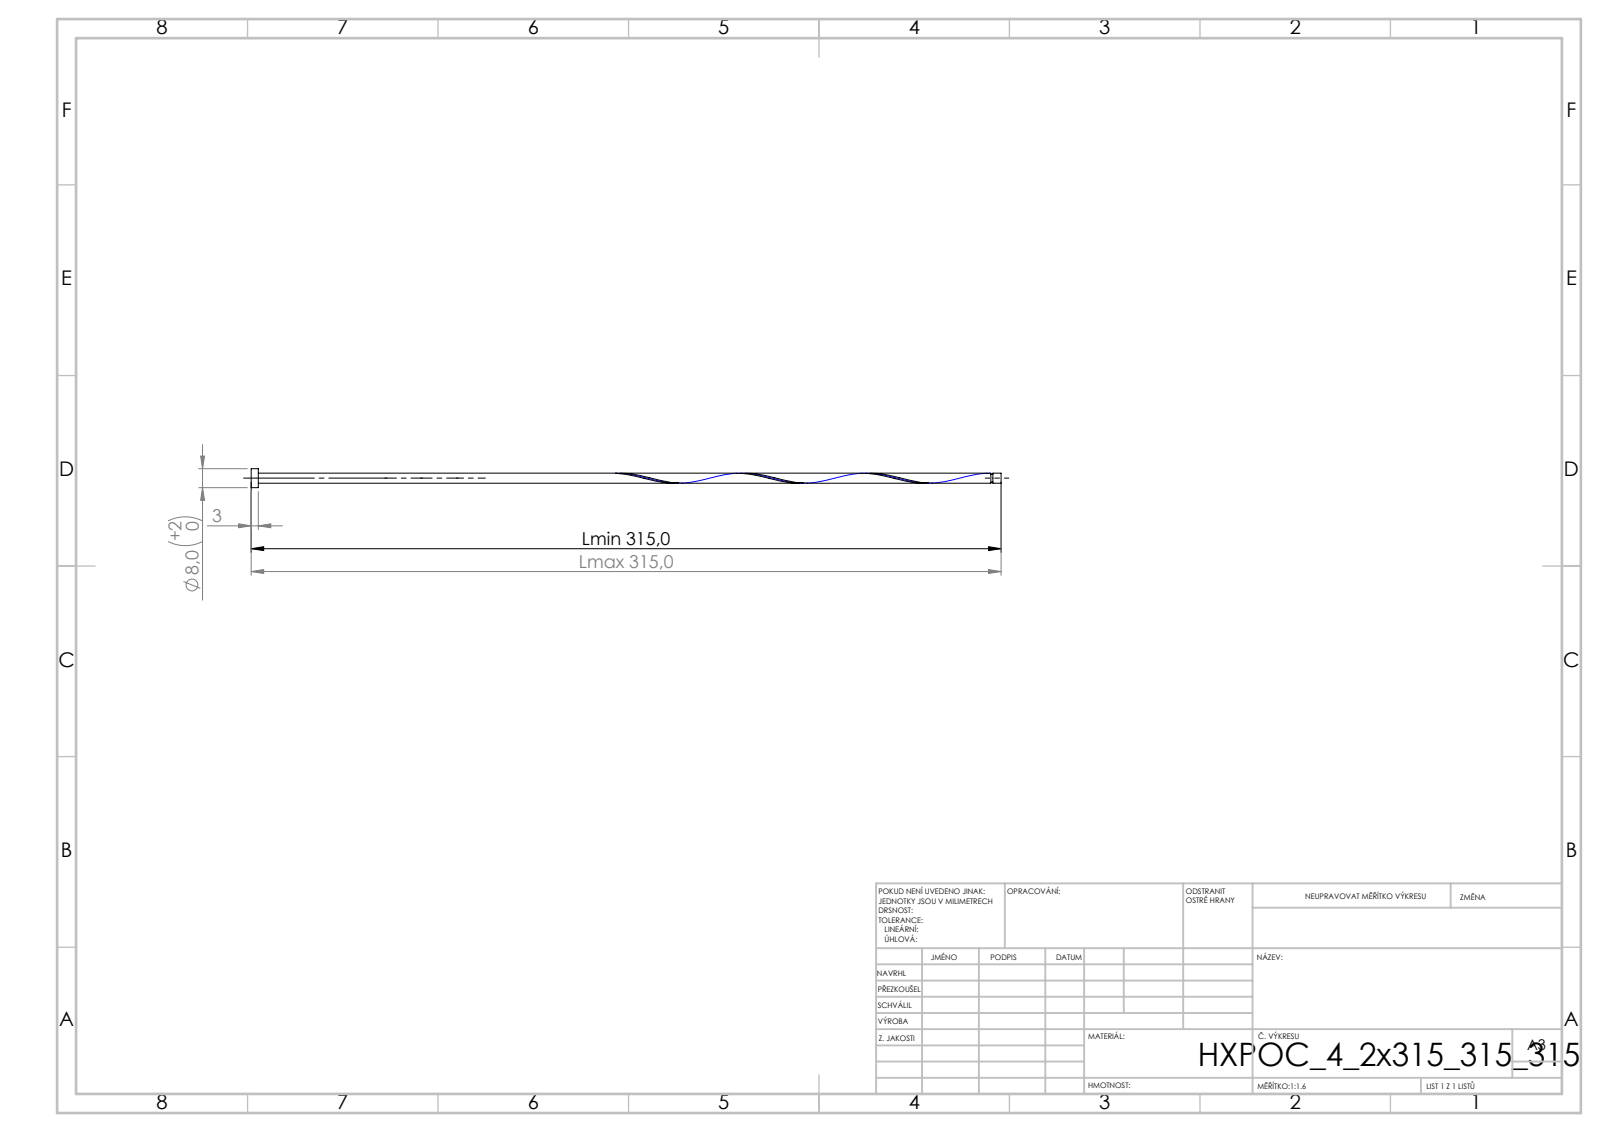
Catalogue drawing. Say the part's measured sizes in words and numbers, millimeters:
Its 3-D file was written by "SolidWorks 2019 (CONFIG_CONTROL_DESIGN)". It is 1 solid with 16 faces: 6 planar, 9 cylindrical and 1 other. Overall it measures 315 by 8 by 8 millimeters. Its volume is 5 397 cubic millimeters and its surface area 5 751 square millimeters. Round bosses or shafts: 1 of diameter 8, 1 of diameter 4.2, 1 of diameter 3.36. The main face-to-face distances are 3, 315, 312, 311.54, 308.54, 3.46, 310.7, 307.7, 0.84, 4.3.
